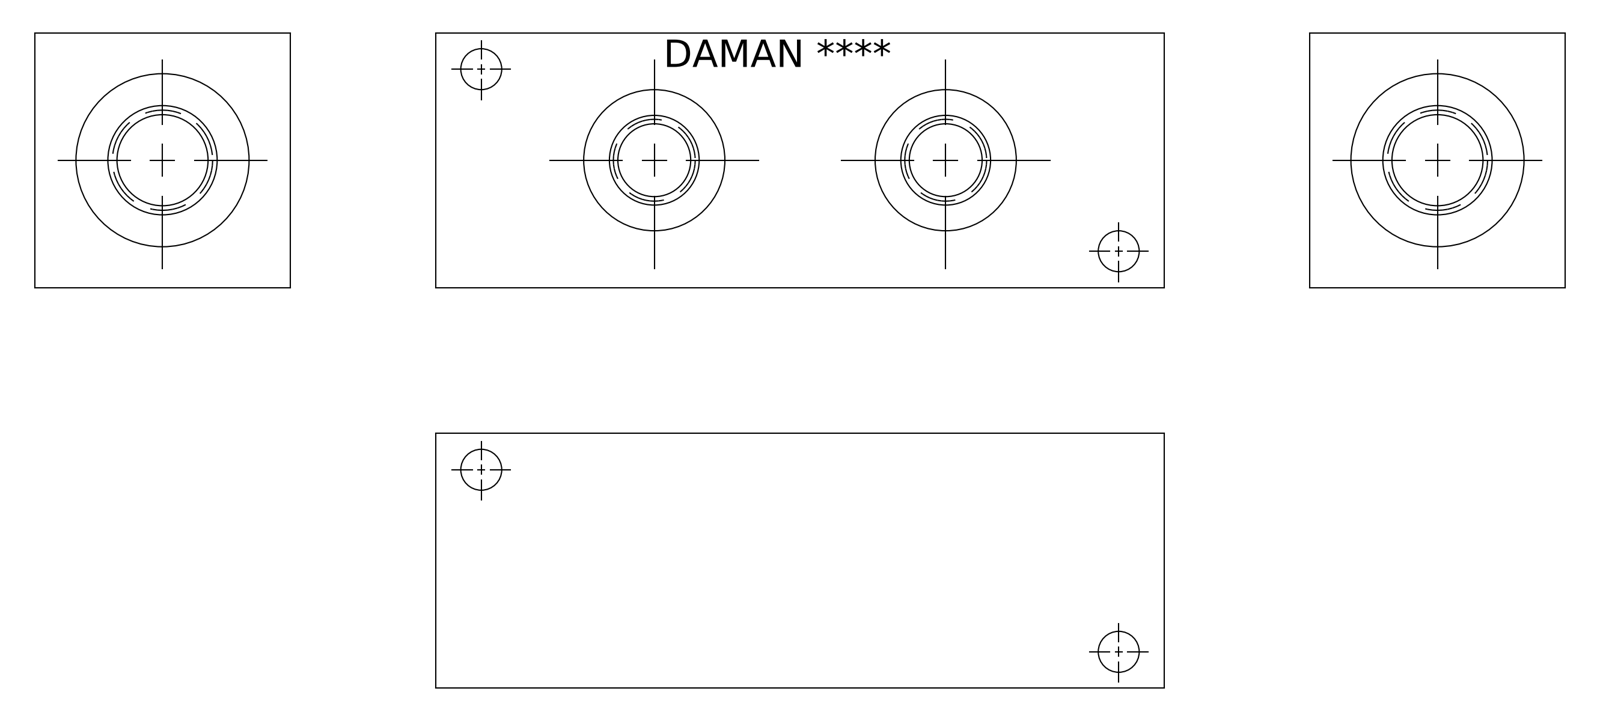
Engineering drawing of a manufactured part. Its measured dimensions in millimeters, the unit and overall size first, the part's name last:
Units: millimetres
Overall size (bounding box): 127 × 44.45 × 44.45
Round holes (diameter × count): ⌀7.14 ×4, ⌀12.29 ×2, ⌀14.27 ×2, ⌀14.53 ×2, ⌀25.02 ×2, ⌀12.9 ×1, ⌀12.9 ×1, ⌀15.88 ×1, ⌀17.5 ×1, ⌀19.05 ×1, ⌀19.25 ×1, ⌀30.63 ×1
Main face-to-face distances: 44.45, 0.79, 127, 126.21, 43.66, 125.42, 43.45, 1, 15.06, 111.94
Hole centre spacings: 34.1, 82.52, 115.61, 50.8
Volume: 223 802 mm³ · Surface area: 34 661 mm²
Bodies: 1 solid, 365 faces (207 planar, 28 cylindrical, 130 other)
Part name (STEP PRODUCT): Part_AH0000206S_3D
STEP written by: Autodesk Inventor 2019 (AUTOMOTIVE_DESIGN)
